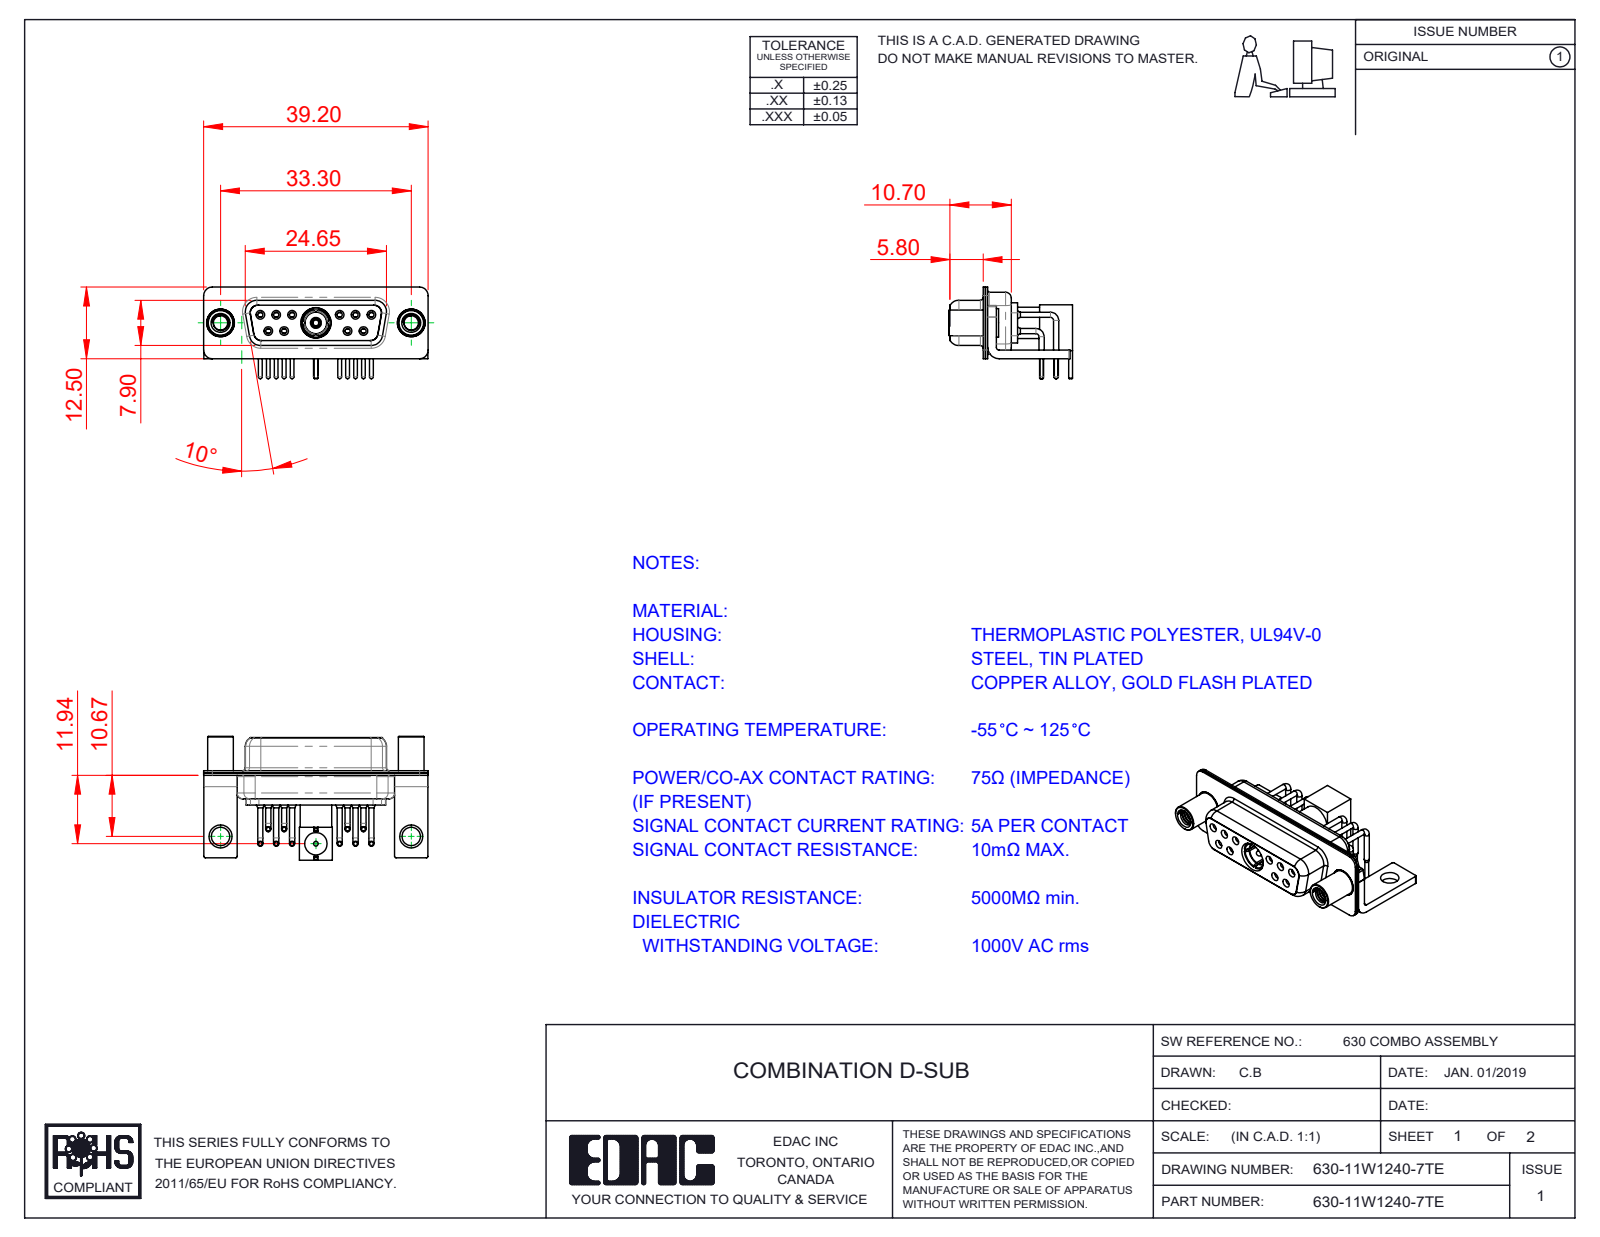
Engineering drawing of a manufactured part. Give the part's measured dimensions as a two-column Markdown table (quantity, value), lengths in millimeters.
| quantity | value |
| --- | --- |
| part name | 630Combo Contact Row 1; 630Combo Stabilizer Bracket; RA Back Shell; Locking Collar (+8 more) |
| STEP written by | SolidWorks 2020 (CONFIG_CONTROL_DESIGN) |
| units | millimeters |
| bodies | 23 solids, 1075 faces (306 planar, 504 cylindrical, 265 other) |
| overall size | 39.2 × 21.61 × 16 |
| volume | 3 196 mm³ |
| surface area | 7 818 mm² |
| round holes (diameter × count) | 1.1 × 11, 1.5 × 11, 0.9 × 10, 2 × 10, 1.7 × 6, 1.6 × 4, 4.85 × 3, 2.5 × 2, 3.2 × 2, 4 × 2, 4.05 × 2, 0.8 × 1 |
| round bosses / shafts (diameter × count) | 0.9 × 10, 0.65 × 10, 1.6 × 6, 5 × 3, 4.95 × 2, 4.8 × 2, 4.5 × 2, 5.5 × 1 |
| partial cylindrical surfaces (radius × count) | 0.25 × 16, 1.5 × 16, 2 × 13, 1.35 × 12, 1.6 × 8, 0.5 × 5, 0.6 × 4, 0.65 × 4 |
| main face-to-face distances | 0.4, 0.8, 1.4, 0.45, 1.8, 8.45, 8.9, 1.5, 6.2, 2.3 |
| hole center spacings | 3.16, 2.77, 13.85, 11.08, 16.62, 5.03, 5.04, 5.54 |
